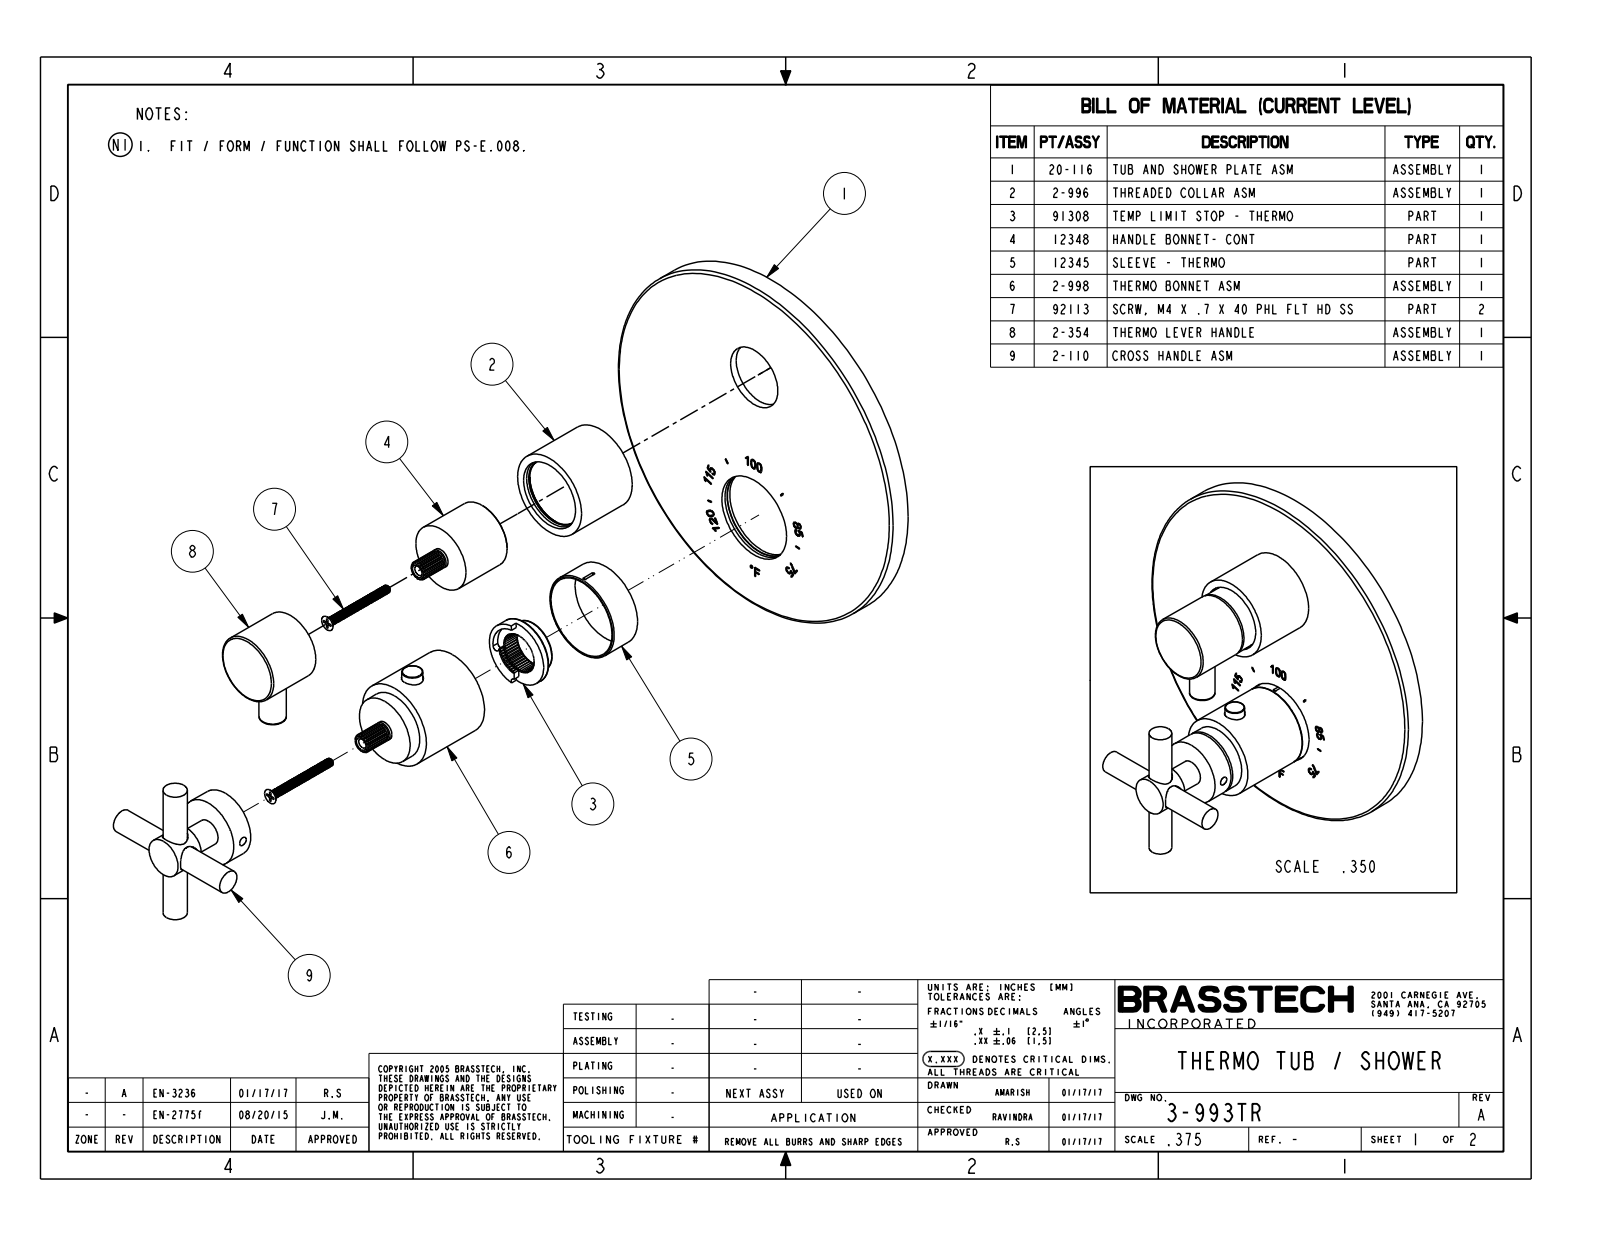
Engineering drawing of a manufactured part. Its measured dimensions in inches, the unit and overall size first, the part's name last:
Units: inches
Overall size (bounding box): 7.09 × 7.09 × 4.698
Round holes (diameter × count): ⌀0.13 ×2, ⌀0.171 ×2, ⌀0.19 ×2, ⌀0.196 ×2, ⌀0.203 ×2, ⌀0.276 ×2, ⌀0.339 ×2, ⌀0.47 ×2, ⌀0.063 ×1, ⌀0.079 ×1, ⌀0.1 ×1, ⌀0.126 ×1
Round bosses / shafts (diameter × count): ⌀0.25 ×3, ⌀0.157 ×3, ⌀1.654 ×2, ⌀0.512 ×2, ⌀0.5 ×2, ⌀0.445 ×2, ⌀0.37 ×2, ⌀0.303 ×2
Partial cylindrical surfaces — rounded edges, fillets, slot ends (radius × count): R0.039 ×2, R0.075 ×2, R0.082 ×2, R0.125 ×2, R0.164 ×2, R0.187 ×2, R0.547 ×1
Main face-to-face distances: 0.08, 0.173, 0.253, 0.185, 0.358, 0.438, 0.37, 0.05, 2.237, 1.867
Hole centre spacings: 1.1, 0.11, 0.554, 0.555, 0.854, 0.964, 1.021, 1.142
Volume: 10.9 in³ · Surface area: 337.6 in²
Bodies: 31 solids, 2519 faces (769 planar, 876 cylindrical, 874 other)
Part name (STEP PRODUCT): 12347_AF2; H-78_2_FEET_AF13; 91678; 20-116_AF2_ASM (+8 more)
STEP written by: PRO/ENGINEER BY PARAMETRIC TECHNOLOGY CORPORATION, 2013150 (CONFIG_CONTROL_DESIGN)
